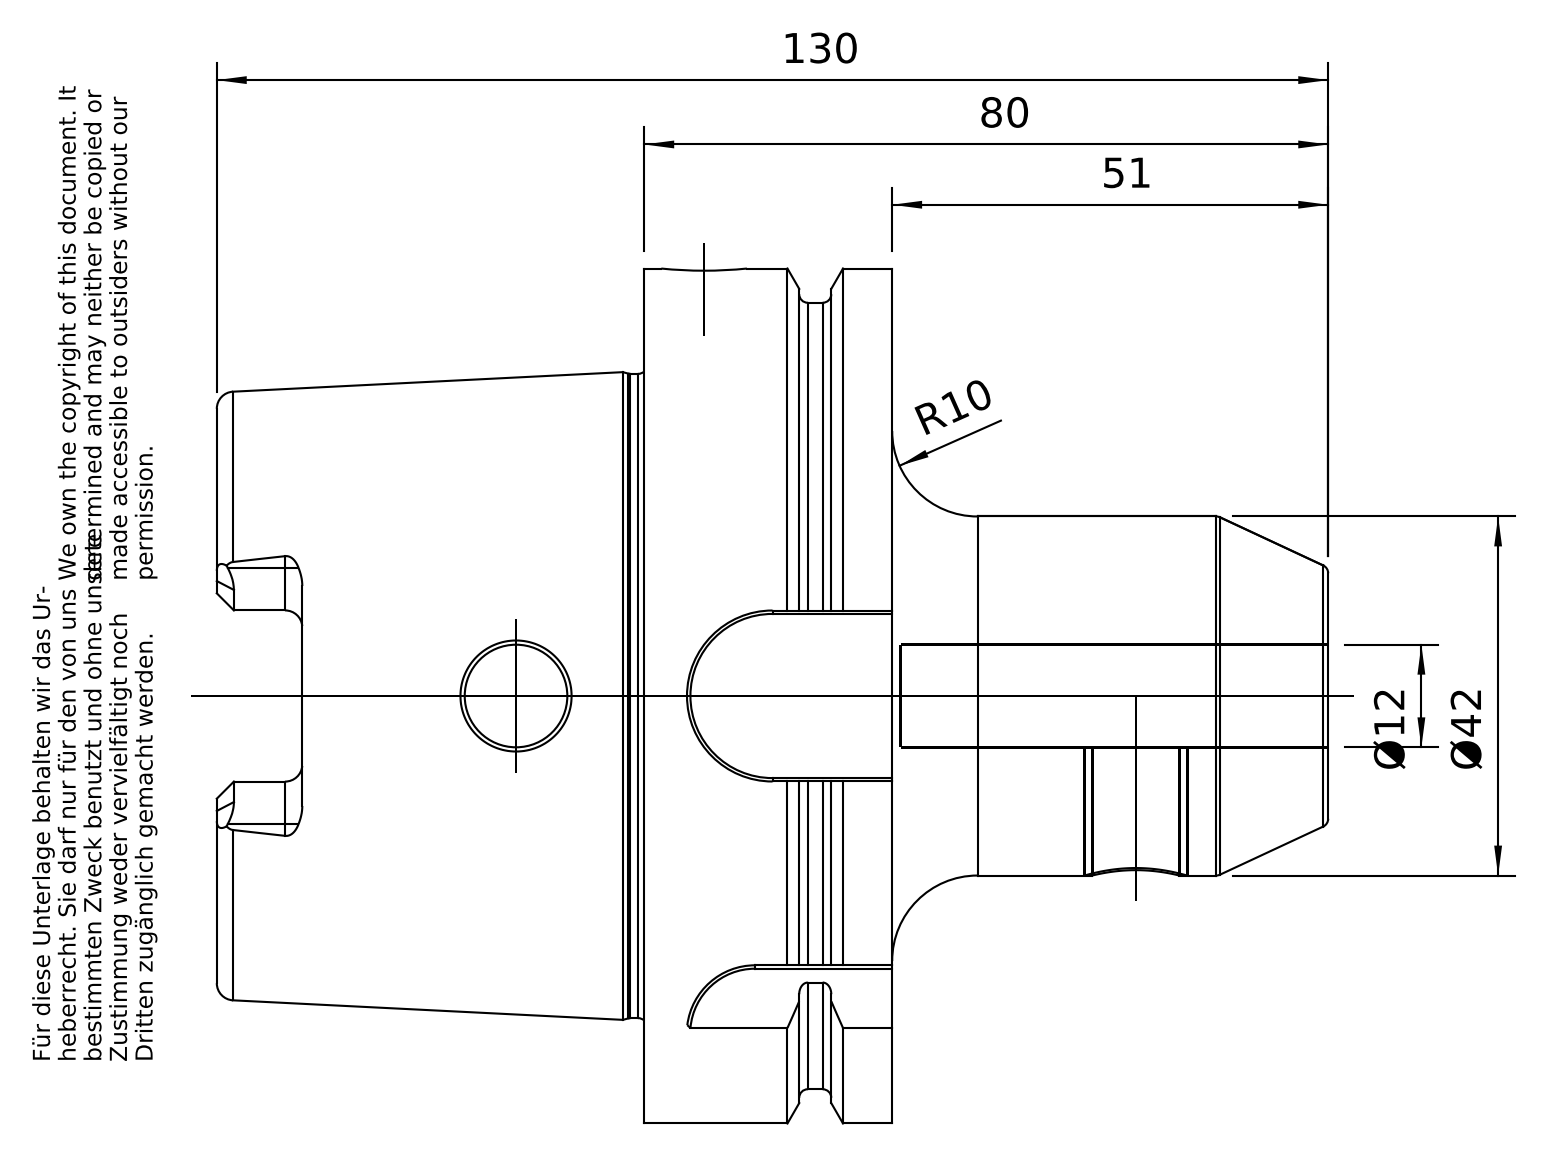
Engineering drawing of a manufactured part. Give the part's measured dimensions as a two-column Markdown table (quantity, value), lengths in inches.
| quantity | value |
| --- | --- |
| part name | A100-000-12 |
| STEP written by | PRO/ENGINEER BY PARAMETRIC TECHNOLOGY CORPORATION, 2010430 (CONFIG_CONTROL_DESIGN) |
| units | inches |
| bodies | 1 solid, 180 faces (50 planar, 55 cylindrical, 75 other) |
| overall size | 5.118 × 3.937 × 3.937 |
| volume | 19.31 in³ |
| surface area | 90.7 in² |
| round holes (diameter × count) | 0.472 × 3, 0.394 × 1, 0.402 × 1, 0.886 × 1, 0.945 × 1, 0.957 × 1, 0.965 × 1, 2.087 × 1, 2.48 × 1 |
| round bosses / shafts (diameter × count) | 3.937 × 1, 3.622 × 1, 2.967 × 1, 1.654 × 1 |
| partial cylindrical surfaces (radius × count) | 0.079 × 6, 0.197 × 4, 0.315 × 1, 0.394 × 1, 0.433 × 1 |
| main face-to-face distances | 1.142, 0.492, 0.65, 1.969, 2.461, 3.11, 3.15, 5.118, 2.657, 2.008 |
| hole center spacings | 1.988 |
